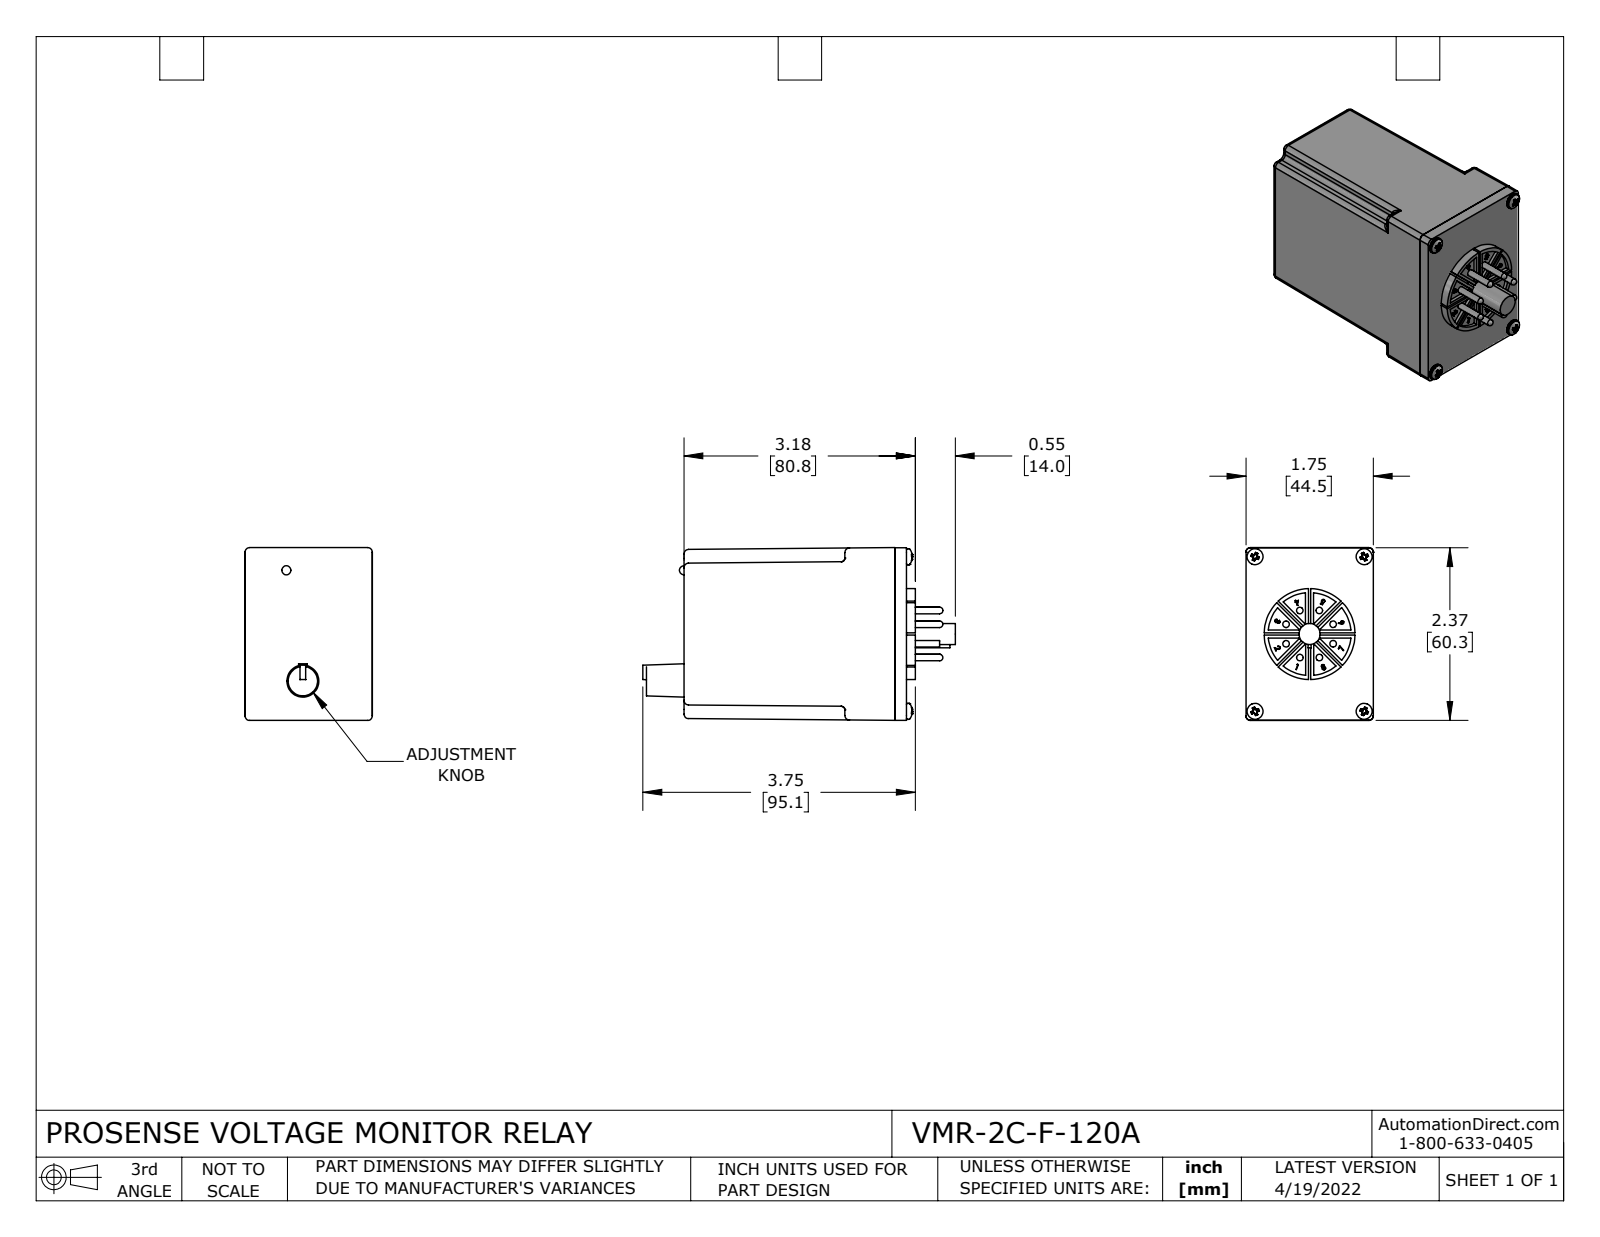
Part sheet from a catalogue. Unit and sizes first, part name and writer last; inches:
Units: inches
Overall size (bounding box): 4.295 × 2.375 × 1.75
Round holes (diameter × count): ⌀0.125 ×4
Round bosses / shafts (diameter × count): ⌀0.09 ×8, ⌀0.219 ×4, ⌀1.25 ×1, ⌀0.29 ×1
Partial cylindrical surfaces — rounded edges, fillets, slot ends (radius × count): R0.063 ×32, R0.005 ×8, R0.05 ×4, R0.57 ×1
Main face-to-face distances: 2.9, 0.16, 3.06, 0.07, 0.23, 3.13, 0.188, 0.05, 0.12, 0.28
Hole centre spacings: 1.5, 2.125, 2.601
Volume: 12.33 in³ · Surface area: 45.79 in²
Bodies: 17 solids, 542 faces (221 planar, 164 cylindrical, 157 other)
Part name (STEP PRODUCT): VMR-2C-F-120A
STEP written by: SolidWorks 2021 (CONFIG_CONTROL_DESIGN)
